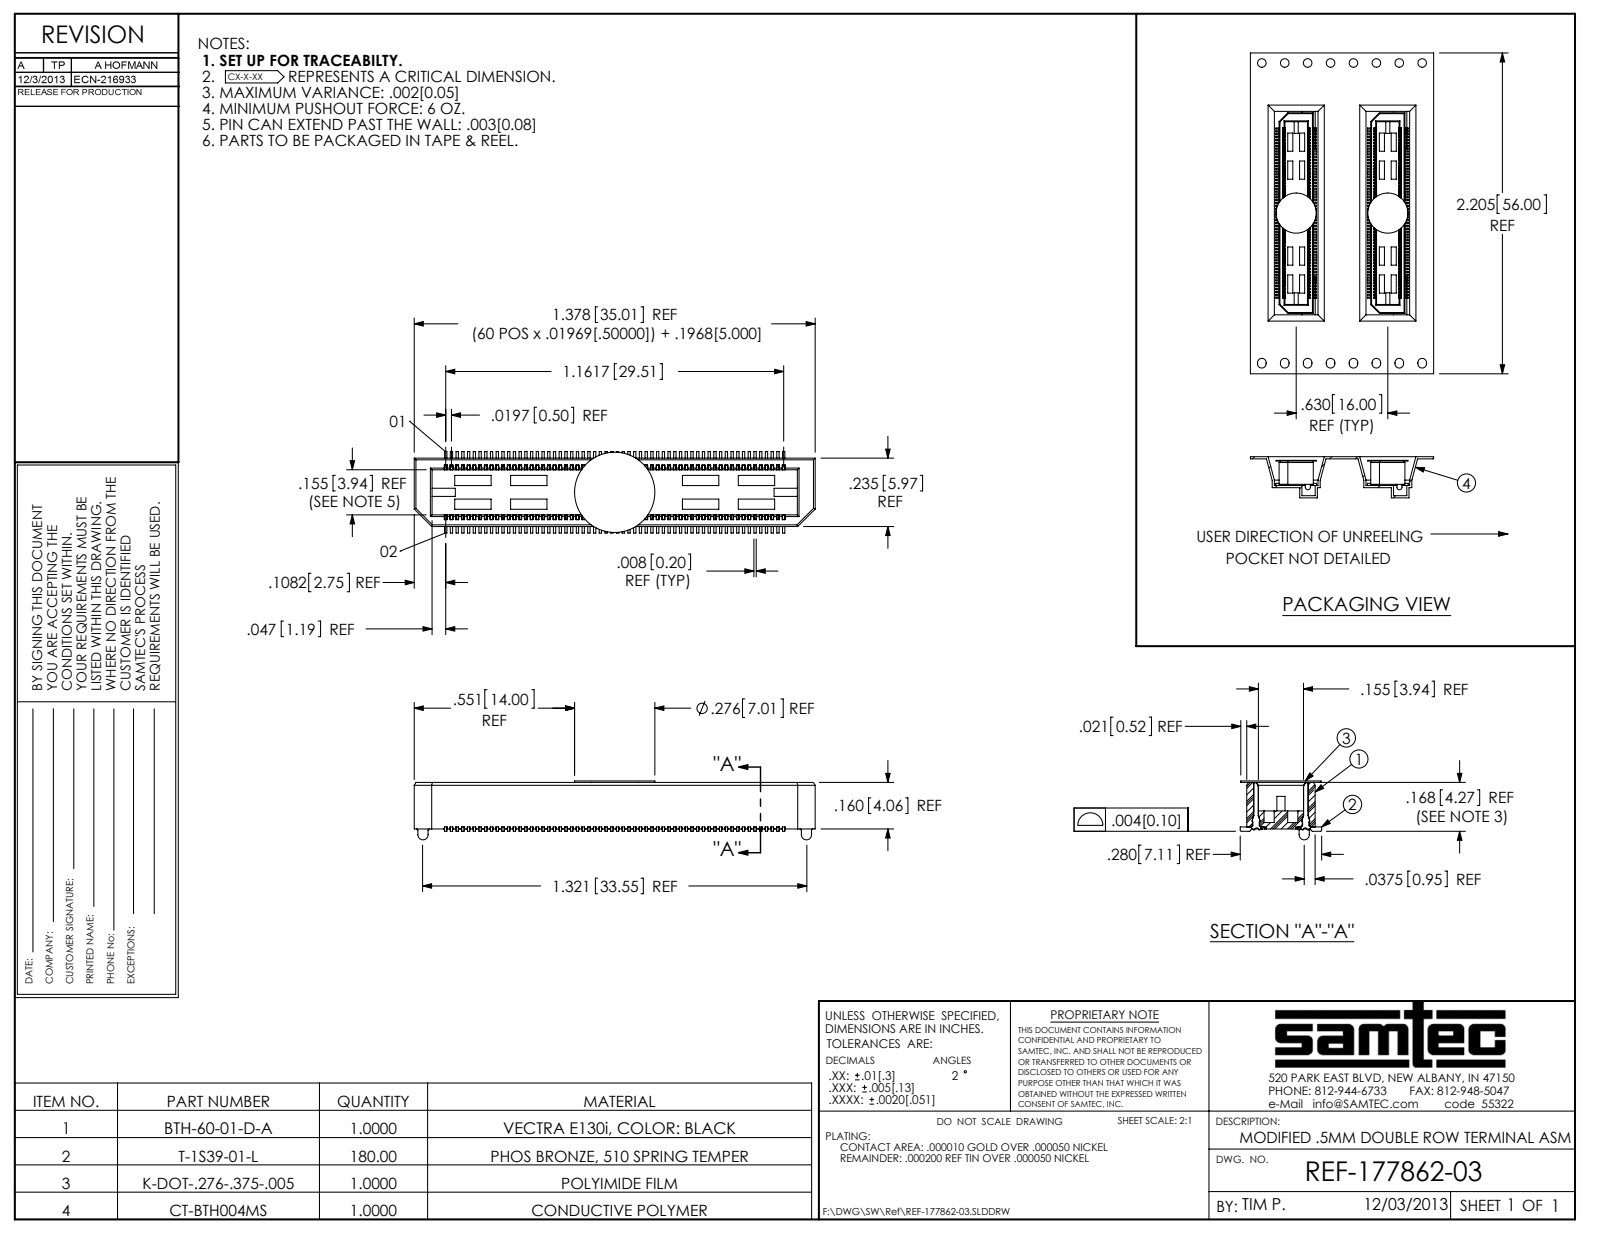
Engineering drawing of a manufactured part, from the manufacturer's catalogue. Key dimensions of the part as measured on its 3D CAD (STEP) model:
Part name (STEP PRODUCT): REF-177862-03
STEP written by: SolidWorks 2014 (CONFIG_CONTROL_DESIGN)
Units: millimetres
Bodies: 1 solid, 8526 faces (6834 planar, 1686 cylindrical, 6 other)
Overall size (bounding box): 35.01 × 7.11 × 5.14
Volume: 483 mm³ · Surface area: 2 372 mm²
Round bosses / shafts (diameter × count): ⌀0.89 ×2, ⌀7.01 ×1
Partial cylindrical surfaces — rounded edges, fillets, slot ends (radius × count): R0.1 ×14, R0.13 ×8, R0.18 ×2
Main face-to-face distances: 1.01, 5.96, 0.39, 4.36, 1.57, 0.62, 1, 0.49, 0.42, 4.95
